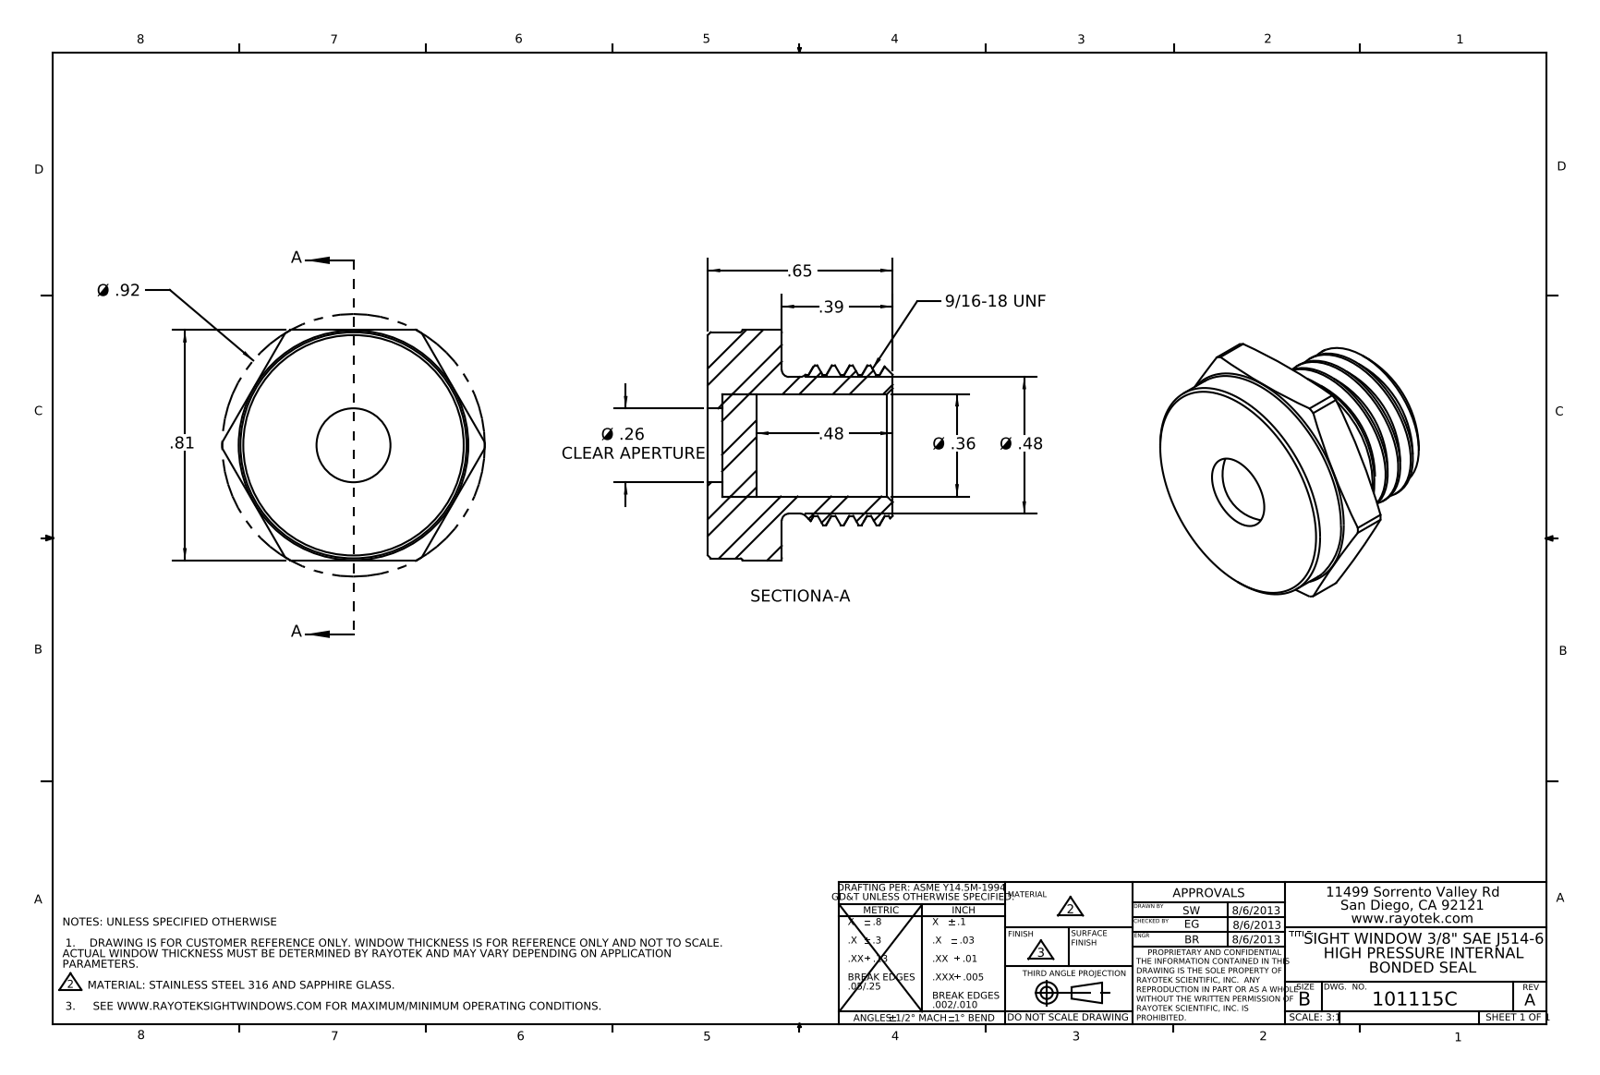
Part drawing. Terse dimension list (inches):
name: 403115
written by: SolidWorks 2012 (AUTOMOTIVE_DESIGN)
unit: in
bodies: 2 solids, 60 faces (12 planar, 26 cylindrical, 22 other)
size: 0.923 × 0.81 × 0.65
volume: 0.169 in³; area: 3.643 in²
holes: 1× ⌀0.26, 1× ⌀0.36
bosses: 1× ⌀0.795, 1× ⌀0.563, 1× ⌀0.481
rounds: 1× R0.462
face distances: 0.26, 0.81, 0.21, 0.05, 0.09, 0.12, 0.17, 0.39, 0.48, 0.6
